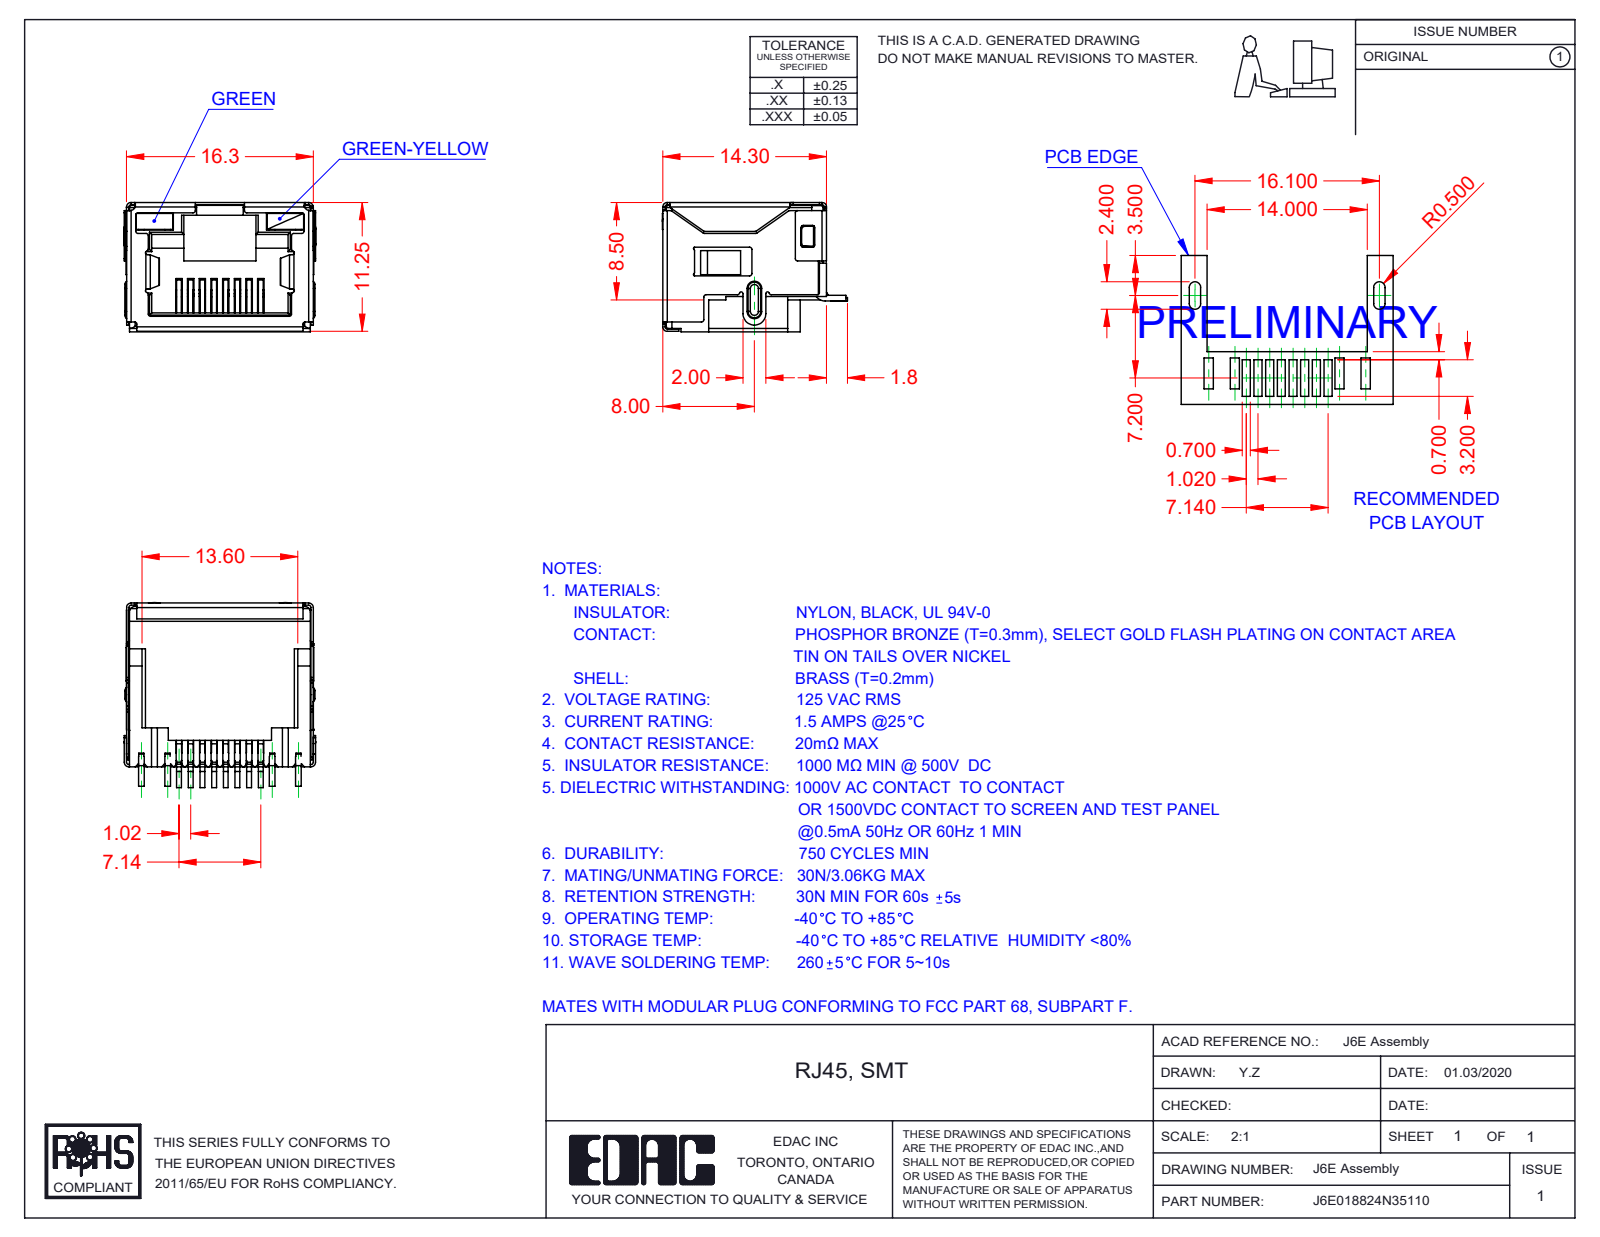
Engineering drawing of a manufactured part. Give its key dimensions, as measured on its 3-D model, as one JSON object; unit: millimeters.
{"part_name": "6E LED RH_5-Green-Yellow; 6E Shield_LED; 6E LED LH_3-Green; 6E Insulator_LED (+2 more)", "step_written_by": "SolidWorks 2016 (CONFIG_CONTROL_DESIGN)", "units": "millimeters", "bodies": {"solids": 12, "faces": 1498, "planar": 1099, "cylindrical": 349, "other": 50}, "overall_size": [16.75, 16.15, 11.3], "volume_mm3": 1109, "surface_area_mm2": 4045, "partial_cylinders_radius": [[0.2, 82], [0.25, 17], [0.4, 13], [0.5, 13], [0.1, 10], [0.15, 7], [0.3, 4], [1, 3]], "face_to_face_distances": [11.05, 16.05, 16.1, 15.85, 11.1, 11.3, 2.4, 0.7, 9.85, 0.49]}
